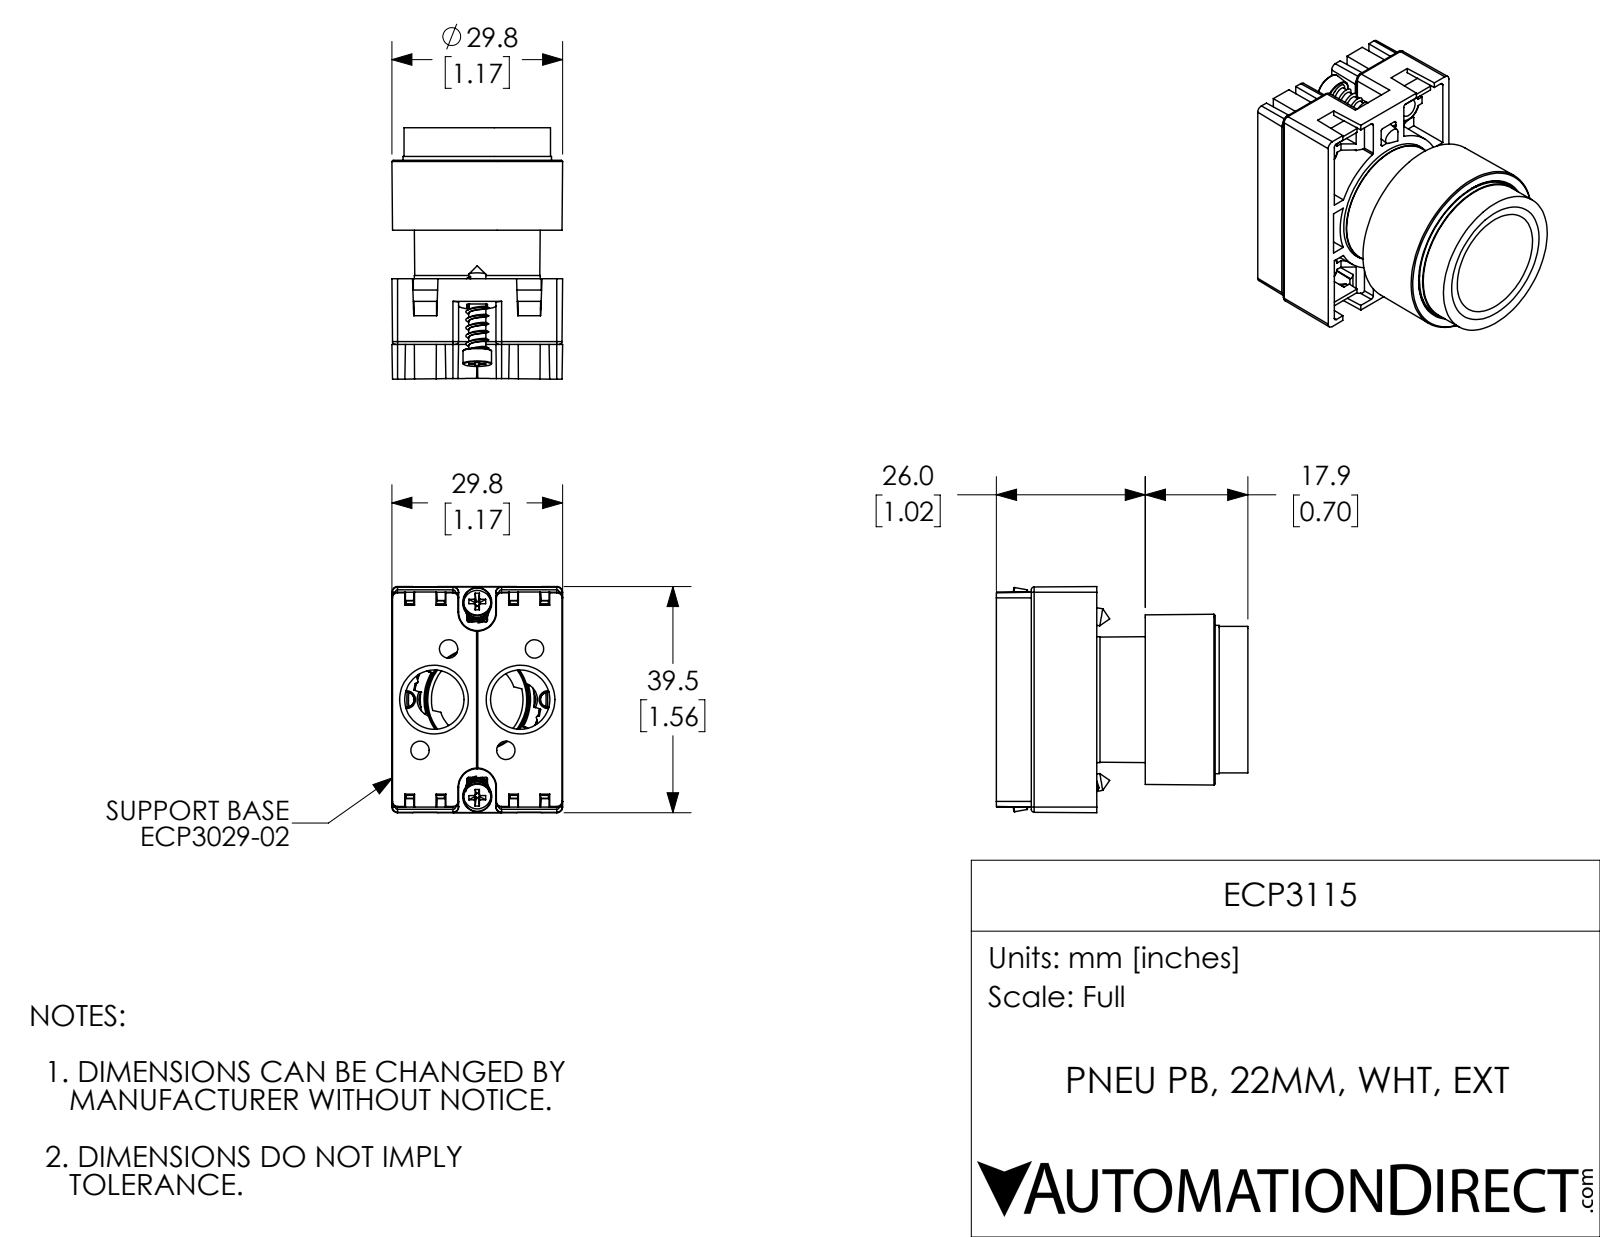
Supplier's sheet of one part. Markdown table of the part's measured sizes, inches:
| quantity | value |
| --- | --- |
| part name | ECP3115 |
| STEP written by | SolidWorks 2017 (AUTOMOTIVE_DESIGN) |
| units | inches |
| bodies | 7 solids, 781 faces (364 planar, 133 cylindrical, 284 other) |
| overall size | 1.728 × 1.555 × 1.173 |
| volume | 1.025 in³ |
| surface area | 29.57 in² |
| round holes (diameter × count) | 0.081 × 4, 0.407 × 2, 0.697 × 1, 0.732 × 1 |
| round bosses / shafts (diameter × count) | 0.197 × 2, 0.118 × 2, 1.02 × 1, 1.008 × 1, 0.866 × 1 |
| partial cylindrical surfaces (radius × count) | 0.02 × 18, 0.006 × 8, 0.012 × 8, 0.008 × 4, 0.039 × 4, 0.008 × 2, 0.118 × 2, 0.128 × 2 |
| main face-to-face distances | 1.261, 0.177, 0.067, 0.715, 0.962, 0.811, 0.451, 0.587, 0.528, 0.519 |
| hole center spacings | 0.304, 0.541, 0.817, 0.295, 0.472, 0.972, 1.081, 0.591 |
